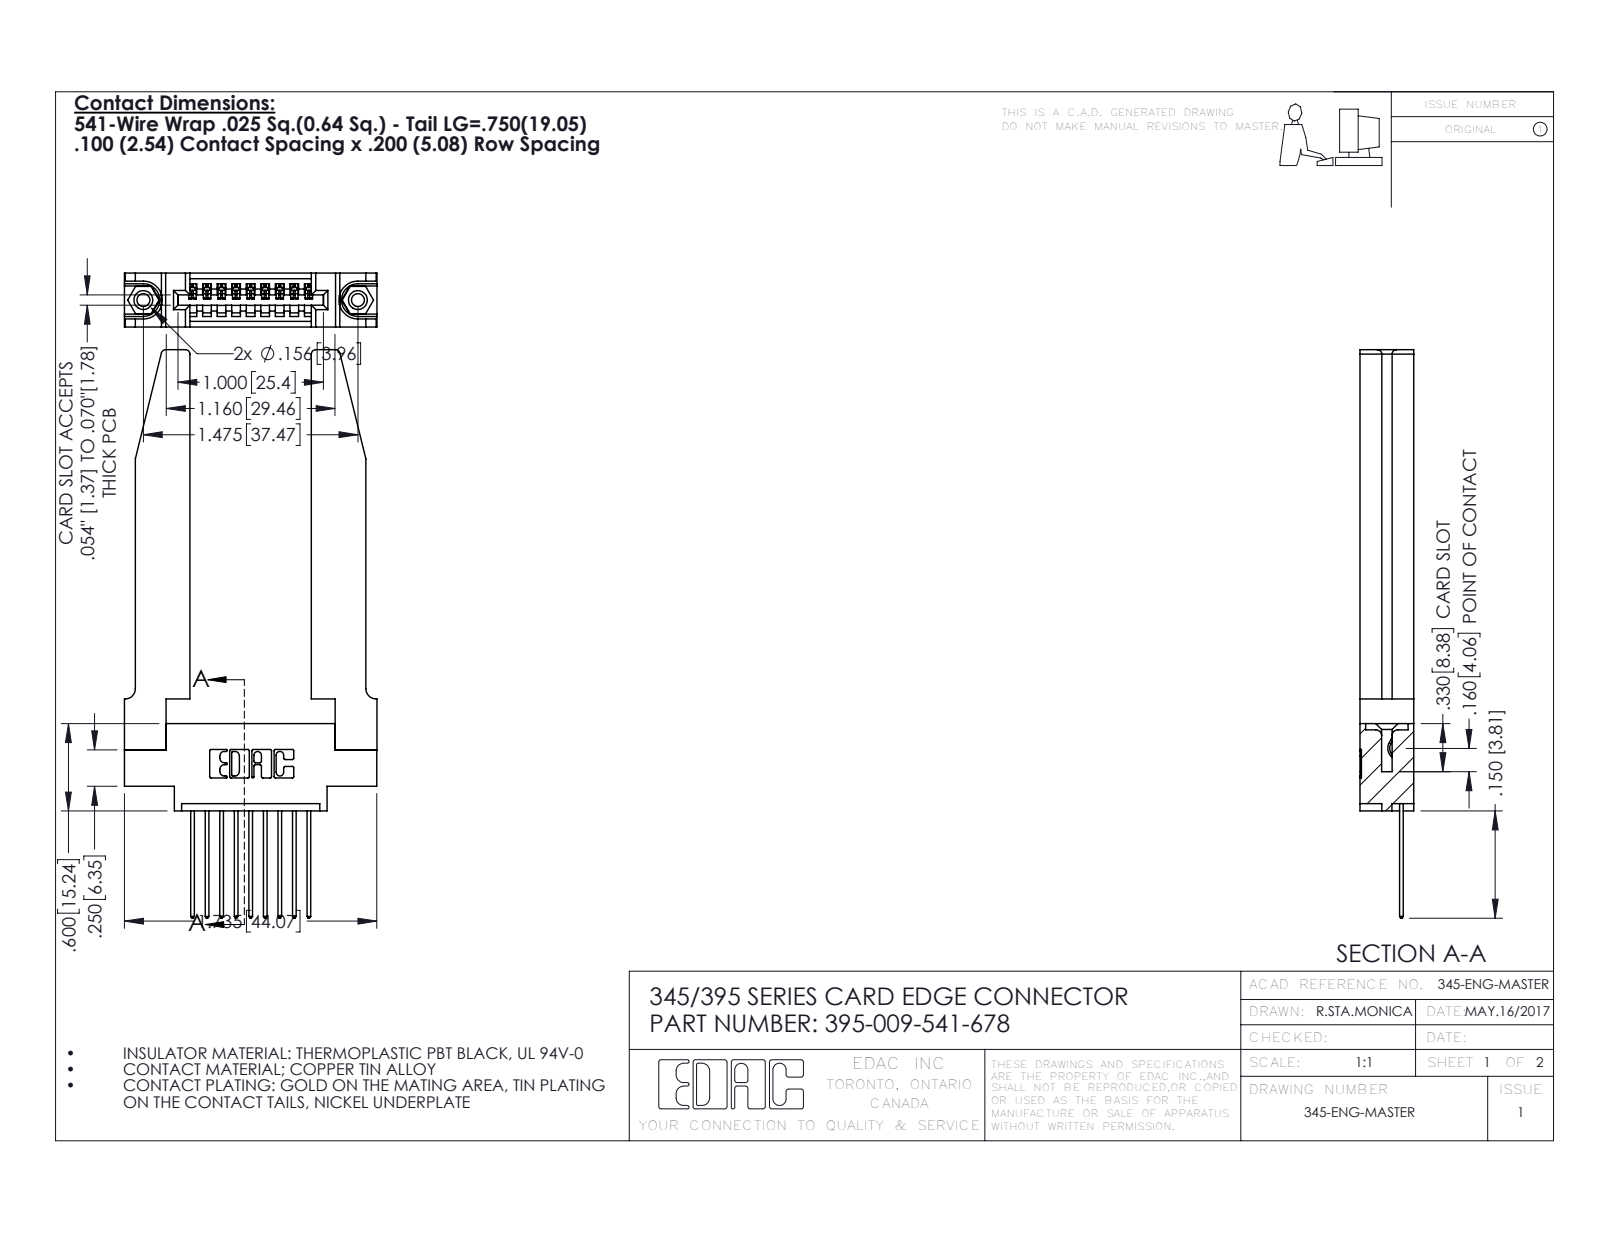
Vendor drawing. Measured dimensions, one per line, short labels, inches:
name: 345 Part_0.170 Offset - 0.156 Dia-TH; 345-250-001_345-250-001-102; 345-220-078_345-220-078; 345-292-001_345-293-141 (+1 more)
written by: SolidWorks 2016 (CONFIG_CONTROL_DESIGN)
unit: in
bodies: 14 solids, 886 faces (586 planar, 248 cylindrical, 52 other)
size: 3.907 × 1.736 × 0.37
volume: 0.708 in³; area: 18.28 in²
holes: 2× ⌀0.089, 2× ⌀0.125, 2× ⌀0.156, 1× ⌀0.064
bosses: 2× ⌀0.155
rounds: 22× R0.01, 18× R0.006, 18× R0.01, 8× R0.03, 6× R0.007, 6× R0.031, 3× R0.026, 2× R0.031
face distances: 0.37, 0.072, 0.298, 0.15, 0.148, 0.22, 0.077, 0.835, 0.098, 0.272
hole spacings: 0.27, 1.244, 1.475
